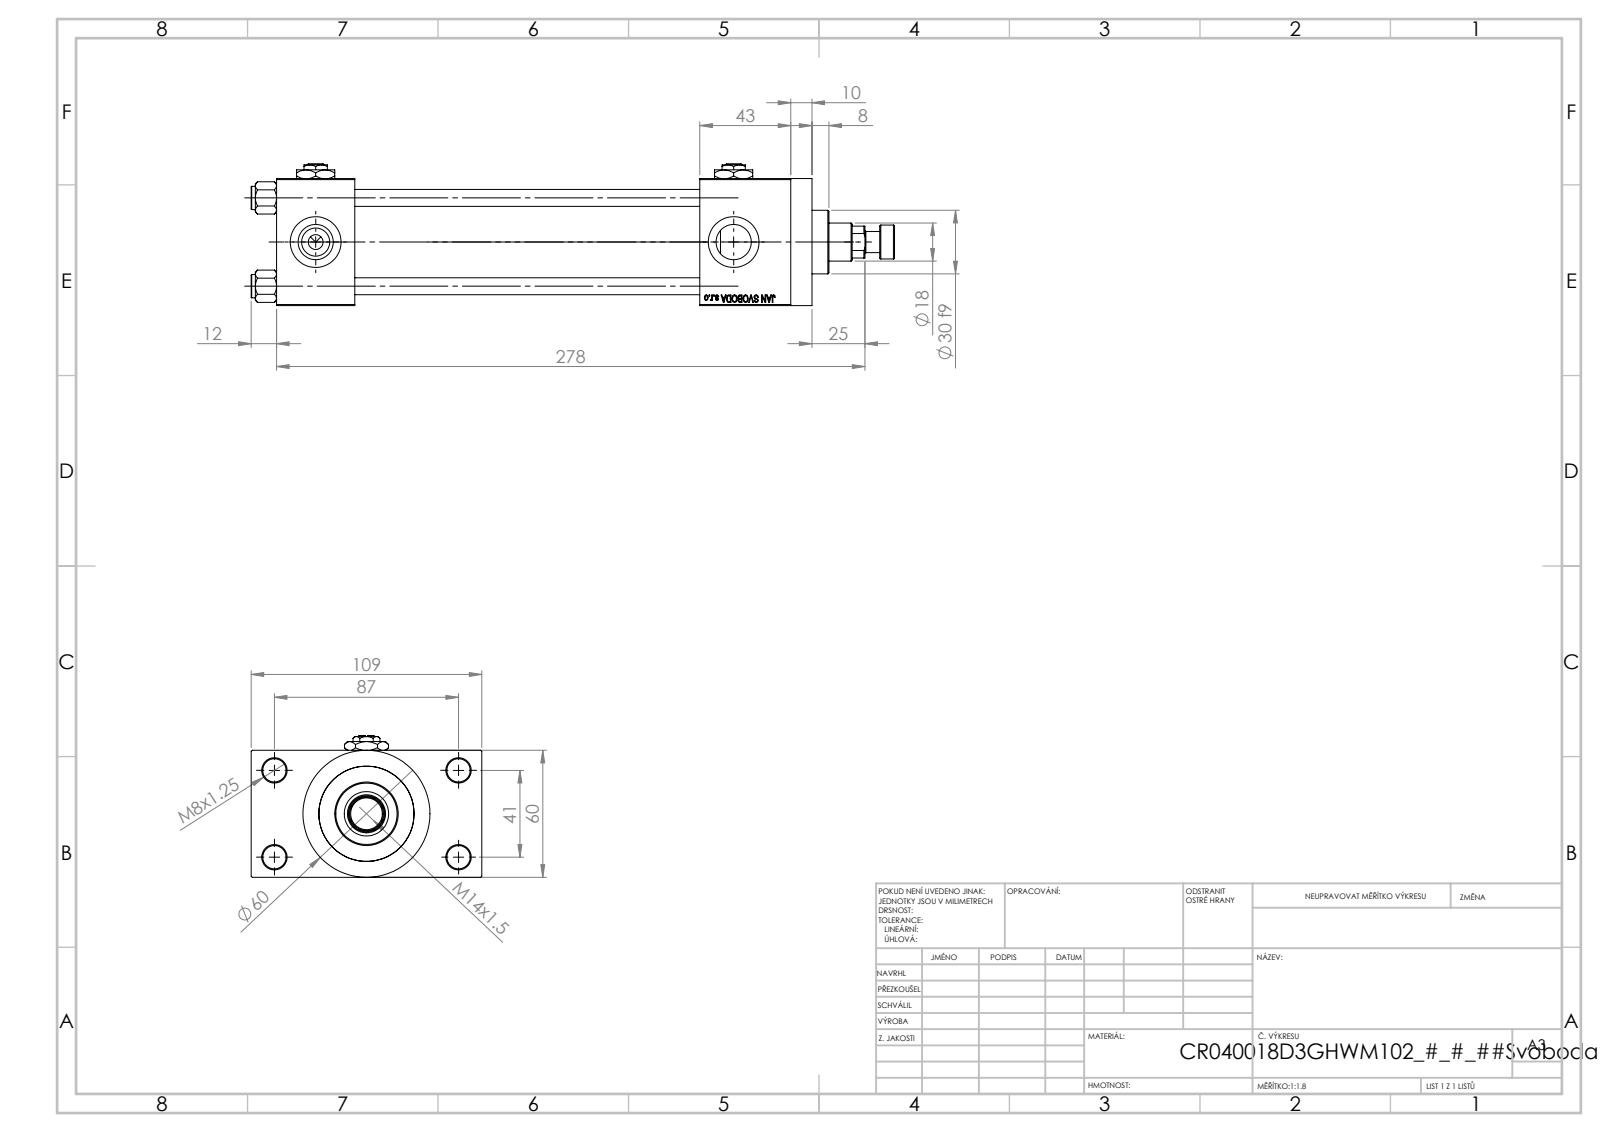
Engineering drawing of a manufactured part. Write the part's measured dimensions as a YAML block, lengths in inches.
part_name: "NUT_M5_D; V215CR_D_TYCINKA; V215CR_ROD_END_W; V215_VC_A (+3 more)"
step_written_by: "SolidWorks 2019 (CONFIG_CONTROL_DESIGN)"
units: inches
bodies: {solids: 14, faces: 1218, planar: 549, cylindrical: 103, other: 566}
overall_size: [11.969, 4.291, 2.638]
volume: 36.78
surface_area: 265.1
round_holes:
  - {diameter: 0.315, count: 4}
  - {diameter: 0.433, count: 4}
  - {diameter: 0.656, count: 4}
  - {diameter: 0.945, count: 4}
  - {diameter: 0.276, count: 3}
  - {diameter: 0.335, count: 1}
  - {diameter: 0.709, count: 1}
  - {diameter: 0.827, count: 1}
  - {diameter: 1.22, count: 1}
  - {diameter: 1.575, count: 1}
  - {diameter: 1.772, count: 1}
round_bosses_or_shafts:
  - {diameter: 0.433, count: 4}
  - {diameter: 2.362, count: 1}
  - {diameter: 1.811, count: 1}
  - {diameter: 1.181, count: 1}
  - {diameter: 0.63, count: 1}
  - {diameter: 0.394, count: 1}
partial_cylinders:
  - {radius: 0.335, count: 1}
face_to_face_distances: [2.362, 0.965, 6.417, 3.327, 1.457, 7.874, 1.693, 9.567, 8.11, 0.394]
hole_center_spacings: [0.892, 1.161, 1.642, 1.856, 1.893, 2.533, 3.011, 1.614]
